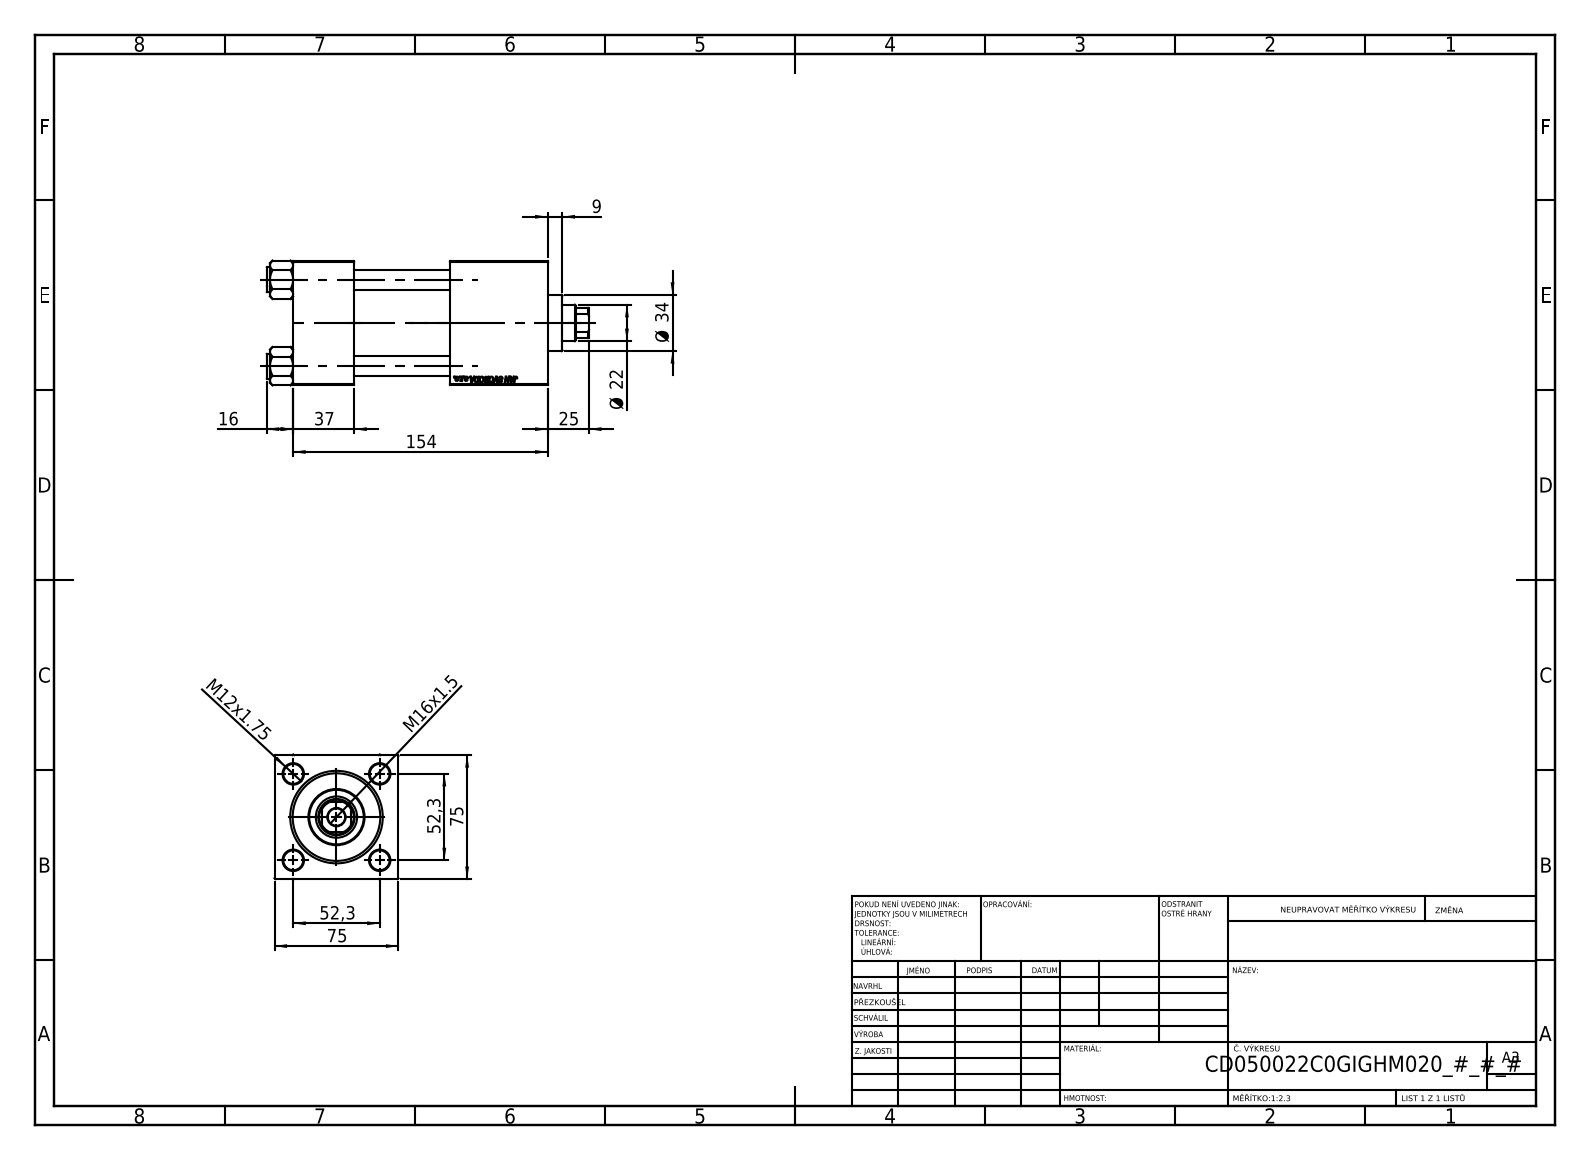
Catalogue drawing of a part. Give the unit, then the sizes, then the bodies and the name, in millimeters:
Units: millimetres
Overall size (bounding box): 195 × 75.54 × 75
Round holes (diameter × count): ⌀12 ×4, ⌀7 ×2, ⌀20.96 ×2, ⌀30 ×2, ⌀10.5 ×1, ⌀22 ×1, ⌀25 ×1, ⌀41 ×1, ⌀50 ×1, ⌀53 ×1
Round bosses / shafts (diameter × count): ⌀15 ×4, ⌀56 ×1, ⌀34 ×1
Partial cylindrical surfaces — rounded edges, fillets, slot ends (radius × count): R10.5 ×1
Main face-to-face distances: 75, 37, 154, 117, 95, 58, 59, 125.3, 88.3, 30.3
Hole centre spacings: 36.98, 52.3, 73.96
Volume: 657 336 mm³ · Surface area: 147 176 mm²
Bodies: 11 solids, 1148 faces (526 planar, 86 cylindrical, 536 other)
Part name (STEP PRODUCT): V215CD_VC_C; V215CD_VCP_C; V215CD_Body_C; NUT_M5_V215CD_C (+1 more)
STEP written by: SolidWorks 2019 (CONFIG_CONTROL_DESIGN)
